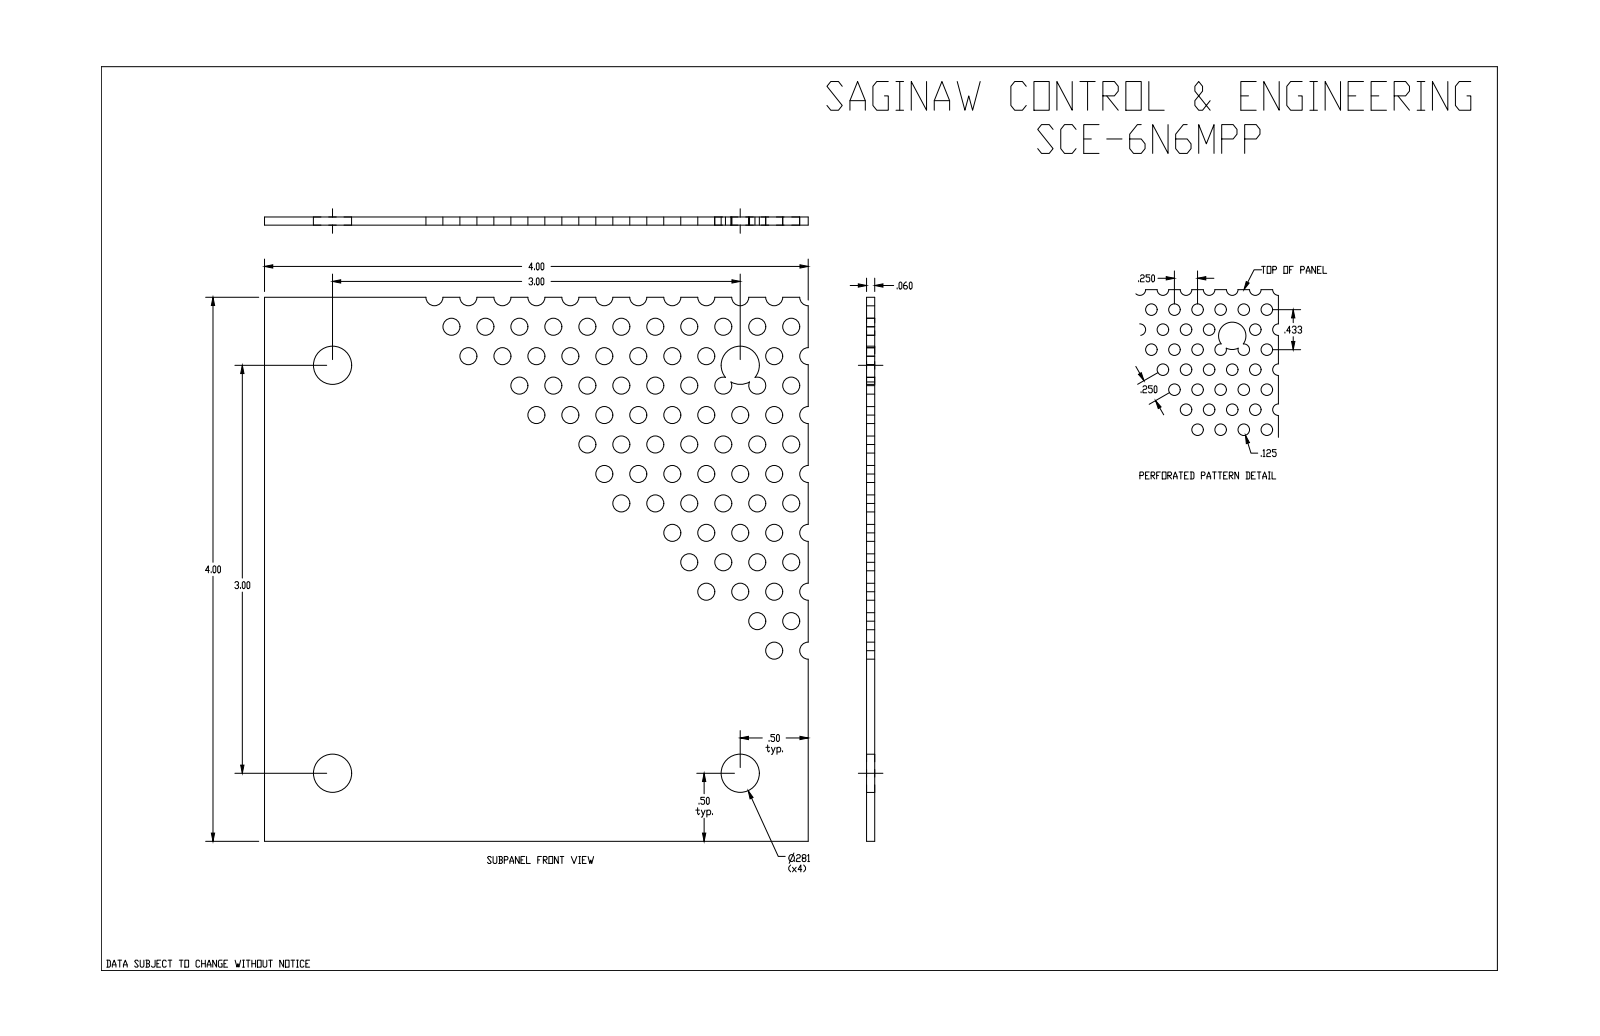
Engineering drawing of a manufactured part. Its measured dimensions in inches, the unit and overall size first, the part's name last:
Units: inches
Overall size (bounding box): 4 × 4 × 0.06
Round holes (diameter × count): ⌀0.125 ×58, ⌀0.125 ×12, ⌀0.281 ×4
Partial cylindrical surfaces — rounded edges, fillets, slot ends (radius × count): R0.062 ×14, R0.063 ×4
Main face-to-face distances: 0.06, 4
Hole centre spacings: 0.25, 0.5, 0.661, 0.433, 0.433, 0.901, 0.75, 1.323
Volume: 0.887 in³ · Surface area: 32.45 in²
Bodies: 1 solid, 116 faces (23 planar, 93 cylindrical, 0 other)
Part name (STEP PRODUCT): SCE-6N6MPP
STEP written by: SolidWorks 2019 (CONFIG_CONTROL_DESIGN)
